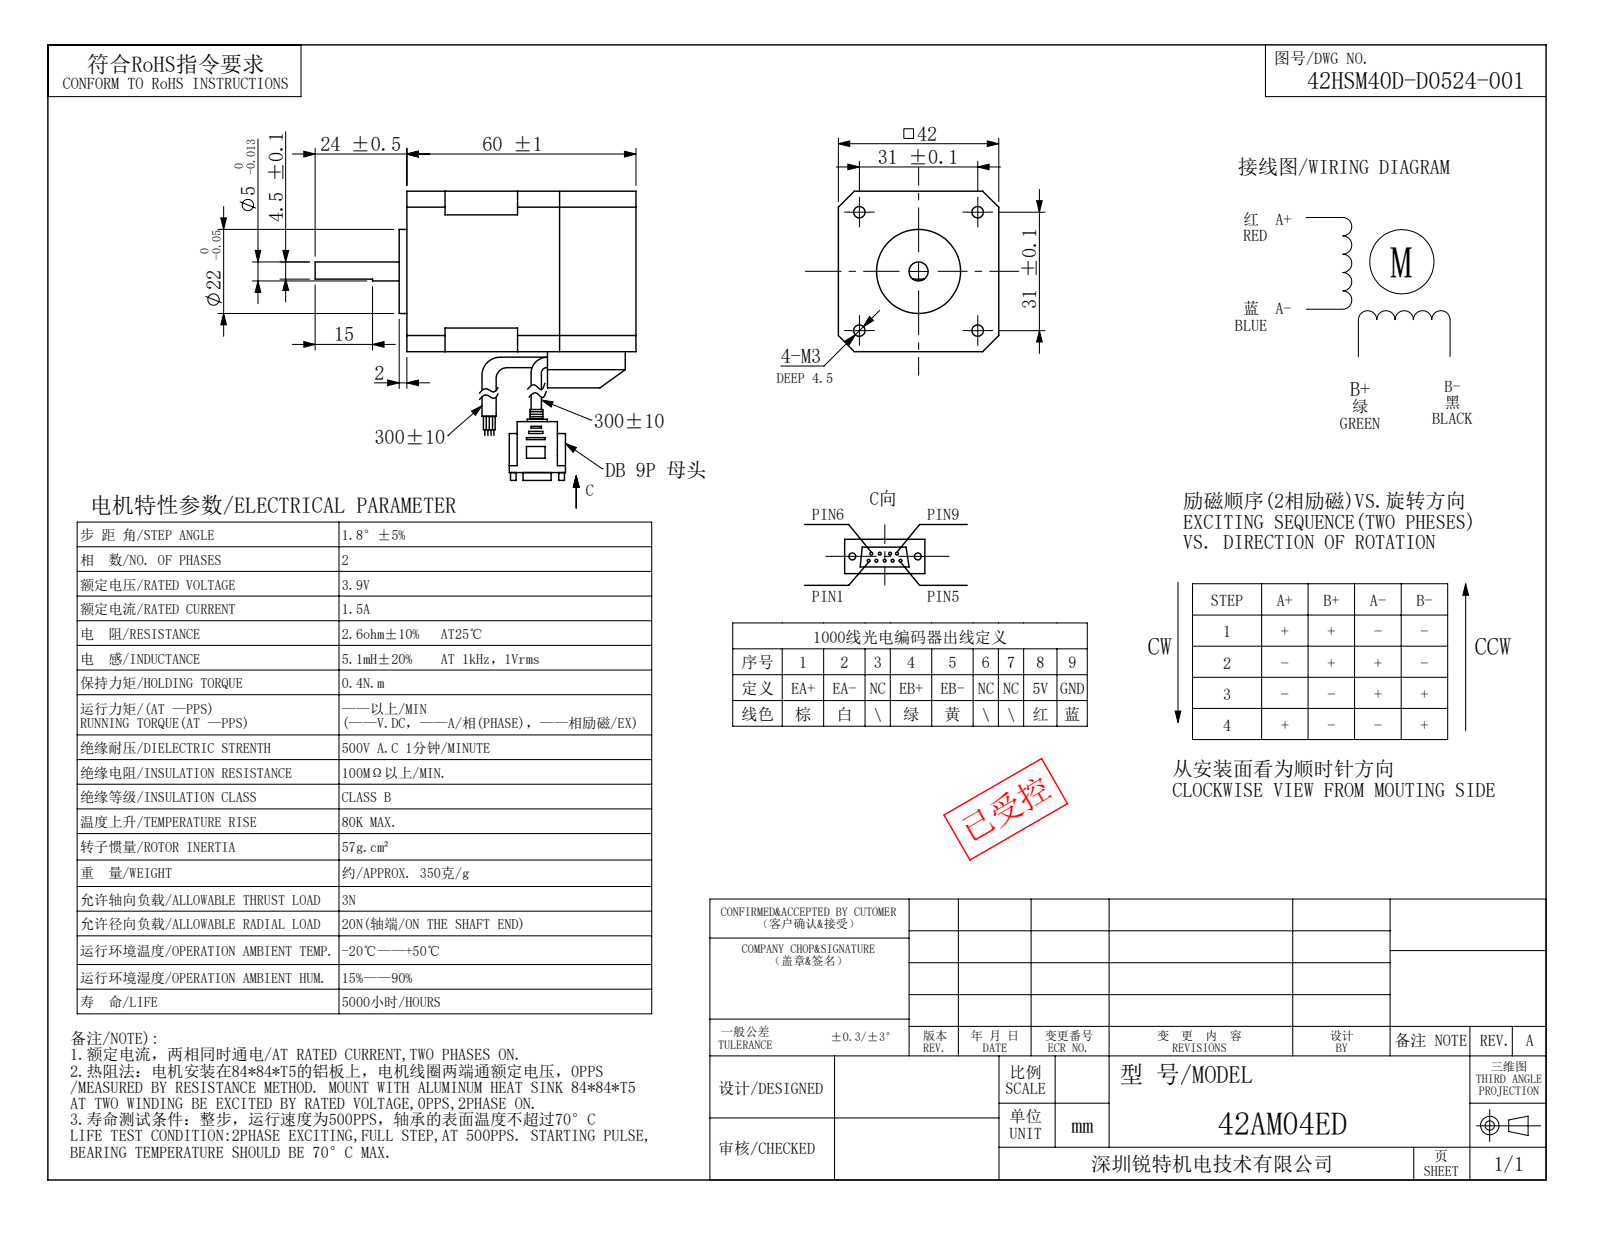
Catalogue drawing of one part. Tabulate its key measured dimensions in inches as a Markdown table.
| quantity | value |
| --- | --- |
| part name | 42HSM40D-D0520-001 |
| STEP written by | SolidWorks 2014 (AUTOMOTIVE_DESIGN) |
| units | inches |
| bodies | 1 solid, 46 faces (34 planar, 12 cylindrical, 0 other) |
| overall size | 3.307 × 1.654 × 1.654 |
| volume | 6.284 in³ |
| surface area | 23.14 in² |
| round holes (diameter × count) | 0.118 × 4 |
| round bosses / shafts (diameter × count) | 0.866 × 1, 0.197 × 1 |
| main face-to-face distances | 1.654, 2.362, 0.056, 2.048, 2.441, 0.079, 1.993, 2.104, 2.104, 2.049 |
| hole center spacings | 1.22, 1.726 |
